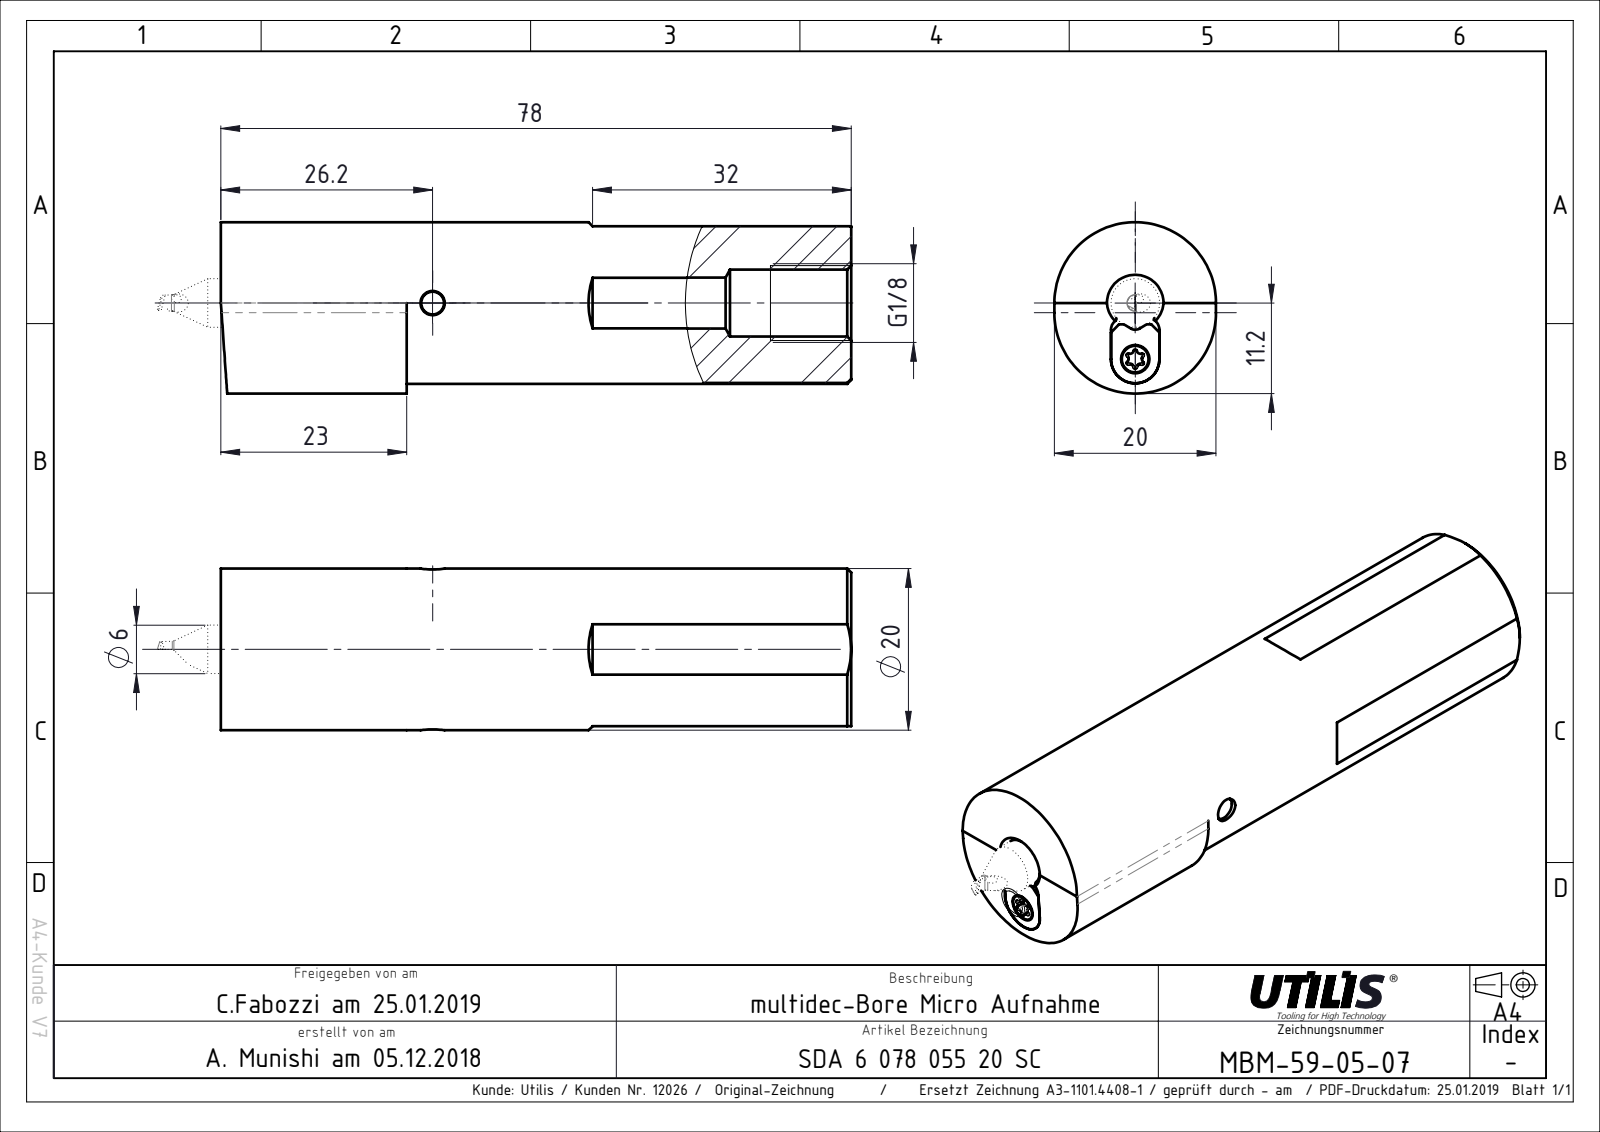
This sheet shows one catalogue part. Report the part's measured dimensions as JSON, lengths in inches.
{"part_name": "UTP AblageMBM-59-05-07", "step_written_by": "SolidWorks 2018 (CONFIG_CONTROL_DESIGN)", "units": "inches", "bodies": {"solids": 1, "faces": 48, "planar": 13, "cylindrical": 17, "other": 18}, "overall_size": [3.071, 0.835, 0.787], "volume_in3": 1.295, "surface_area_in2": 11.71, "round_holes": [[0.118, 1], [0.13, 1], [0.236, 1], [0.276, 1], [0.346, 1]], "round_bosses_or_shafts": [[0.787, 1]], "partial_cylinders_radius": [[0.118, 1], [0.394, 1]], "face_to_face_distances": [3.071, 0.276, 0.512, 0.256, 0.236, 0.492, 0.346, 0.02, 0.768, 0.787]}
